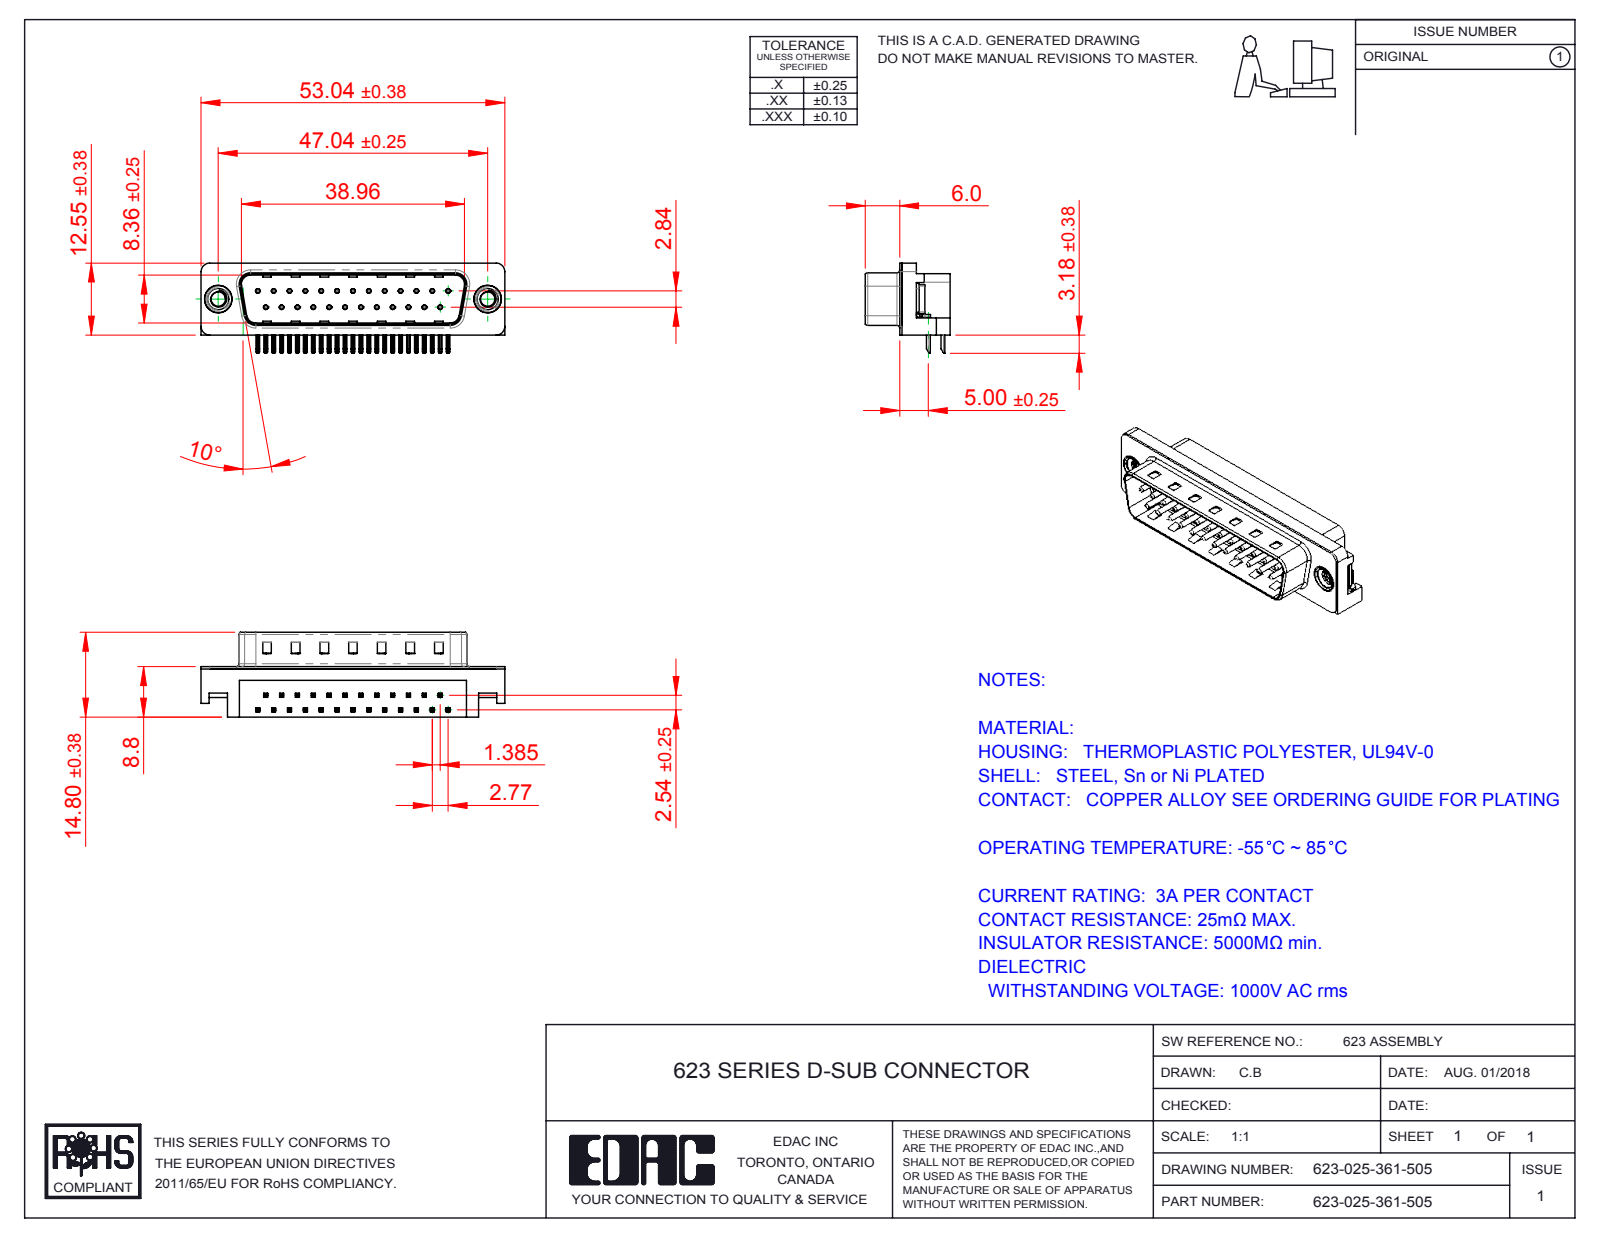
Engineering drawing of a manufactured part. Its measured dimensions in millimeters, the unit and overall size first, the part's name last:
Units: millimetres
Overall size (bounding box): 53.04 × 15.73 × 14.8
Round holes (diameter × count): ⌀0.35 ×25, ⌀0.8 ×25, ⌀2.5 ×2, ⌀4 ×2, ⌀4.8 ×2, ⌀5 ×2
Round bosses / shafts (diameter × count): ⌀0.75 ×25, ⌀4.9 ×2, ⌀4.75 ×2, ⌀3.9 ×2
Partial cylindrical surfaces — rounded edges, fillets, slot ends (radius × count): R0.25 ×108, R0.12 ×50, R1 ×16, R0.5 ×9, R1.5 ×7, R0.9 ×4, R1.6 ×4, R2 ×4
Main face-to-face distances: 0.4, 8.4, 2.1, 1.7, 8.76, 10.46, 10.86, 10.35, 8.8, 5.9
Hole centre spacings: 3.16, 2.77, 11.08, 5.54, 8.31, 5.03, 13.85, 7.48
Volume: 4 719 mm³ · Surface area: 6 720 mm²
Bodies: 31 solids, 2253 faces (1405 planar, 653 cylindrical, 195 other)
Part name (STEP PRODUCT): 623 Housing_25 Socket; 623 M3 Threaded Rivet; 623 Non Board Mount; 623 Contact Top (+3 more)
STEP written by: SolidWorks 2016 (CONFIG_CONTROL_DESIGN)
